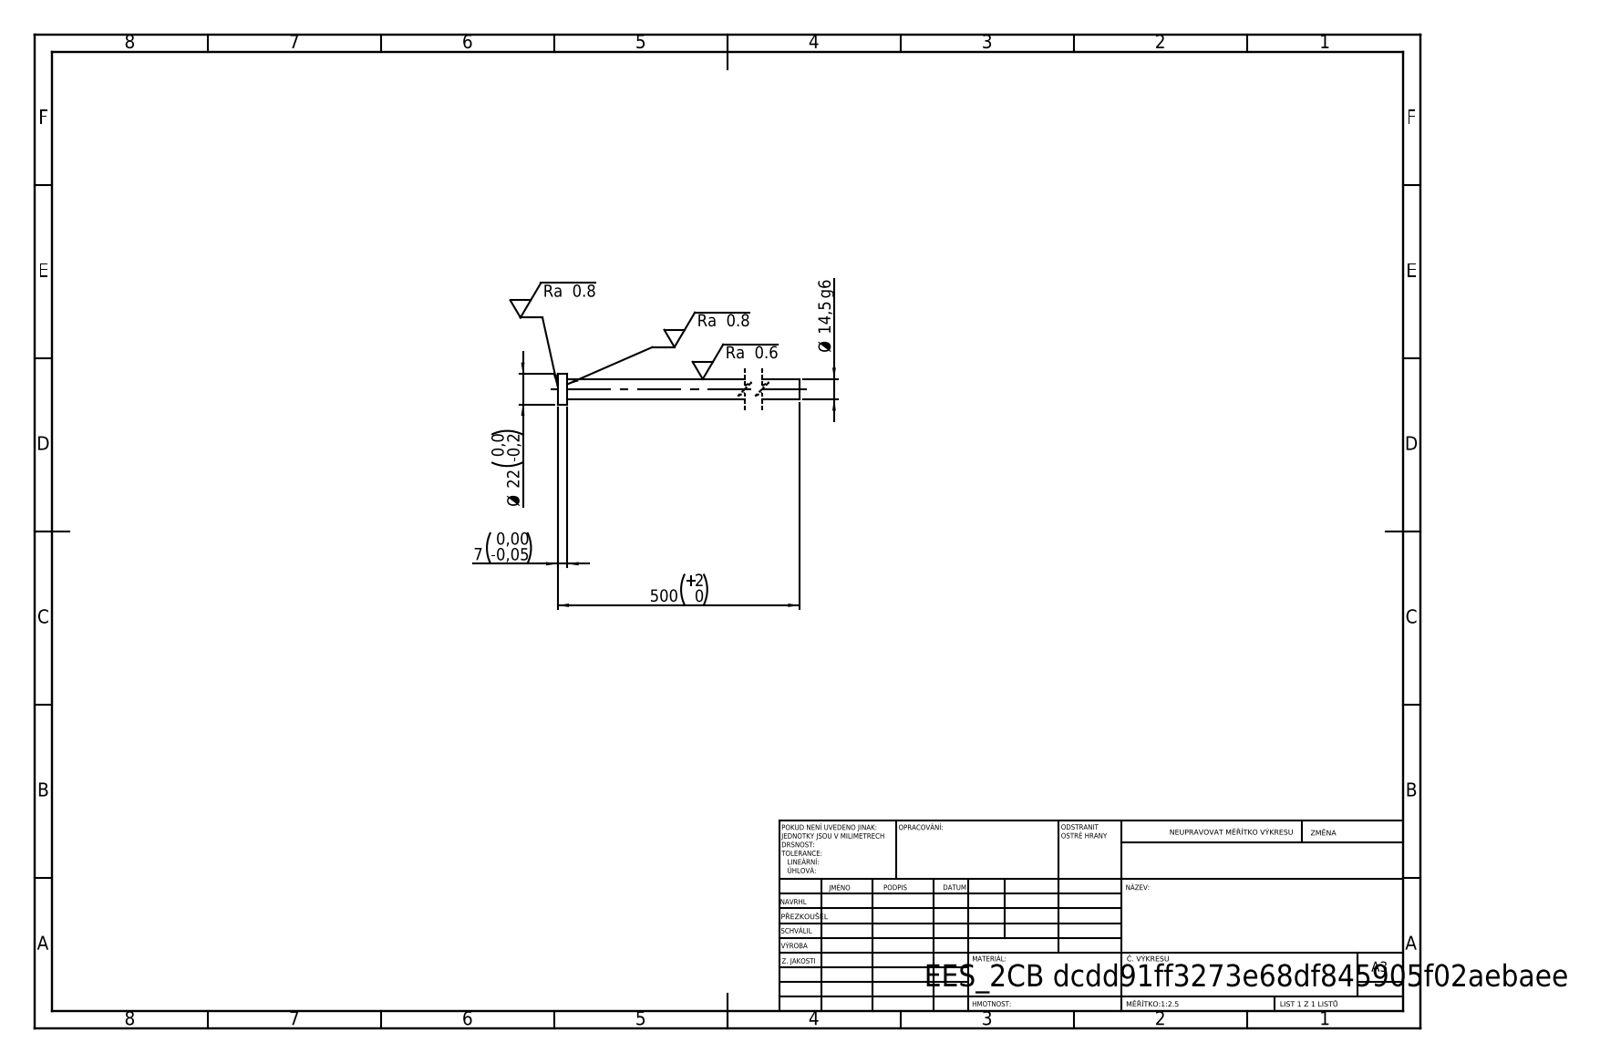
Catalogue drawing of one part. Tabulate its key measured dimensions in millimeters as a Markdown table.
| quantity | value |
| --- | --- |
| STEP written by | SolidWorks 2019 (CONFIG_CONTROL_DESIGN) |
| units | millimeters |
| bodies | 1 solid, 7 faces (3 planar, 4 cylindrical, 0 other) |
| overall size | 500 × 22 × 22 |
| volume | 84 070 mm³ |
| surface area | 23 702 mm² |
| round bosses / shafts (diameter × count) | 22 × 1, 14.5 × 1 |
| main face-to-face distances | 7, 500, 493 |
